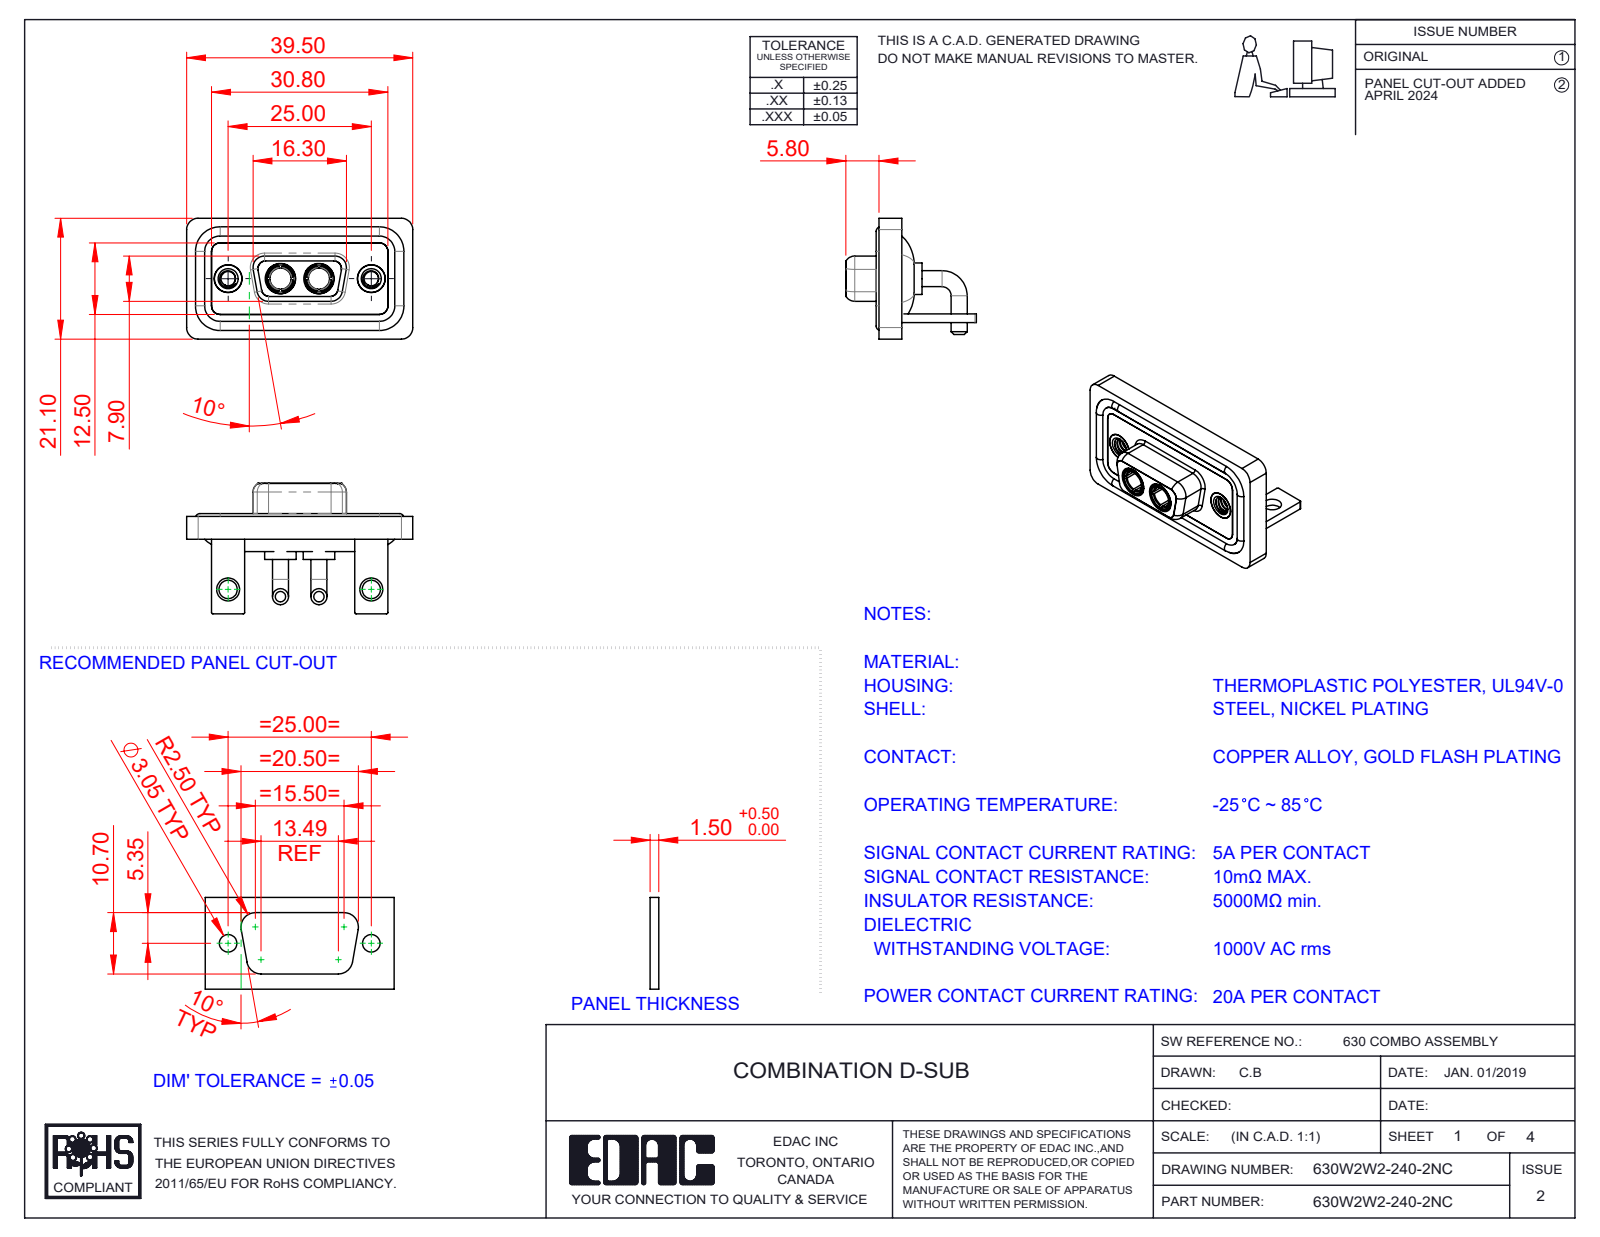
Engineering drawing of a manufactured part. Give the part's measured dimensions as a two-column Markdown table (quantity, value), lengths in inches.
| quantity | value |
| --- | --- |
| part name | 630Combo Housing_2W2; 630Combo Shell Front_09 Contacts; 630Combo Threaded Rivet_A; 630Combo Shell Rear_09 Contacts (+4 more) |
| STEP written by | SolidWorks 2023 (CONFIG_CONTROL_DESIGN) |
| units | inches |
| bodies | 13 solids, 584 faces (183 planar, 260 cylindrical, 141 other) |
| overall size | 1.555 × 0.898 × 0.831 |
| volume | 0.316 in³ |
| surface area | 13.21 in² |
| round holes (diameter × count) | 0.191 × 4, 0.098 × 2, 0.126 × 2, 0.146 × 2, 0.157 × 2, 0.159 × 2, 0.197 × 2, 0.209 × 2 |
| round bosses / shafts (diameter × count) | 0.11 × 4, 0.063 × 4, 0.217 × 2, 0.205 × 2, 0.195 × 2, 0.195 × 2, 0.189 × 2, 0.187 × 2 |
| partial cylindrical surfaces (radius × count) | 0.079 × 19, 0.059 × 18, 0.01 × 16, 0.053 × 8, 0.063 × 8, 0.02 × 5, 0.024 × 4, 0.026 × 4 |
| main face-to-face distances | 0.016, 0.114, 0.059, 0.071, 0.043, 0.146, 0.031, 0.098, 0.063, 0.122 |
| hole center spacings | 0.36, 0.624, 0.984, 0.265 |
